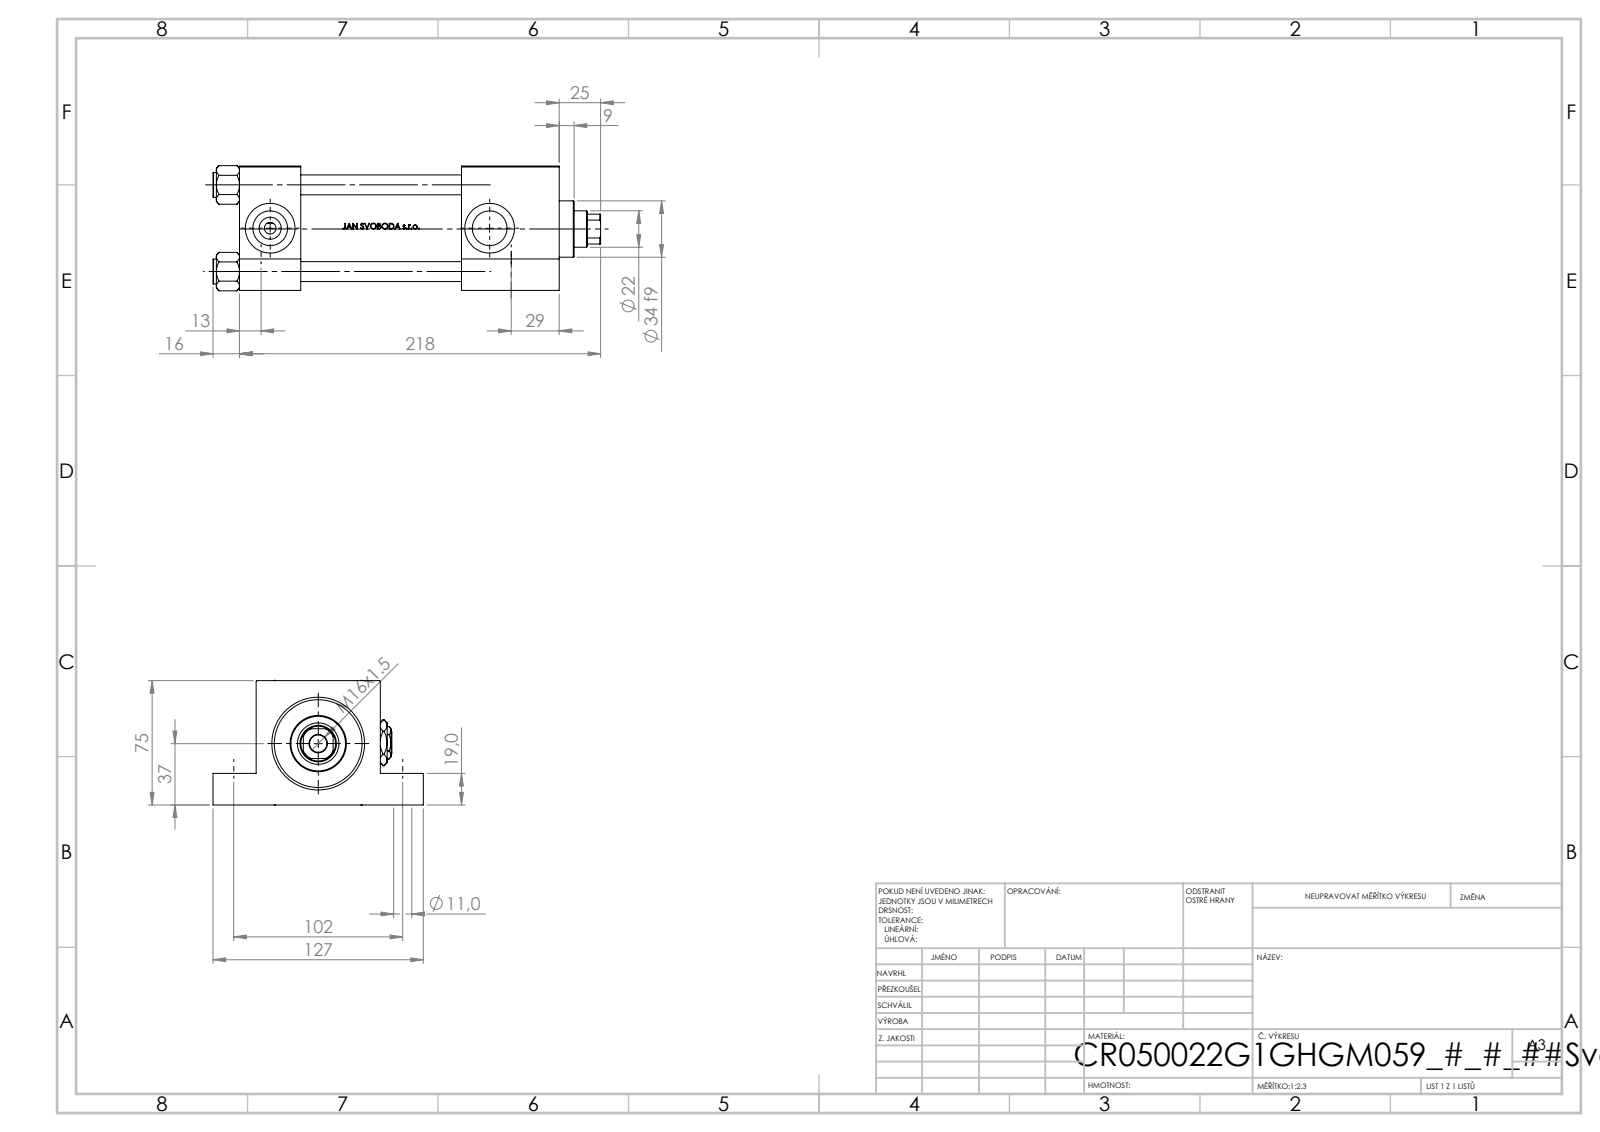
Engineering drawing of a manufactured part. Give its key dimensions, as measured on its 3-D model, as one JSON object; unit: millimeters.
{"part_name": "V215CR_G_Body; Zatka_pro_OIL_PORT; V215_VC_A; V215CR_VCP_G (+2 more)", "step_written_by": "SolidWorks 2019 (CONFIG_CONTROL_DESIGN)", "units": "millimeters", "bodies": {"solids": 12, "faces": 1134, "planar": 454, "cylindrical": 128, "other": 552}, "overall_size": [234, 127, 75.54], "volume_mm3": 804352, "surface_area_mm2": 182868, "round_holes": [[11, 4], [12, 4], [7, 2], [20.96, 2], [30, 2], [10.5, 1], [22, 1], [25, 1], [41, 1], [50, 1], [53, 1]], "round_bosses_or_shafts": [[15, 4], [56, 1], [34, 1]], "partial_cylinders_radius": [[10.5, 1]], "face_to_face_distances": [75, 37, 59, 193, 156, 19, 56, 134, 97, 26], "hole_center_spacings": [52.3, 36.63, 37.34, 73.96, 102, 151, 182.22, 132.5]}
